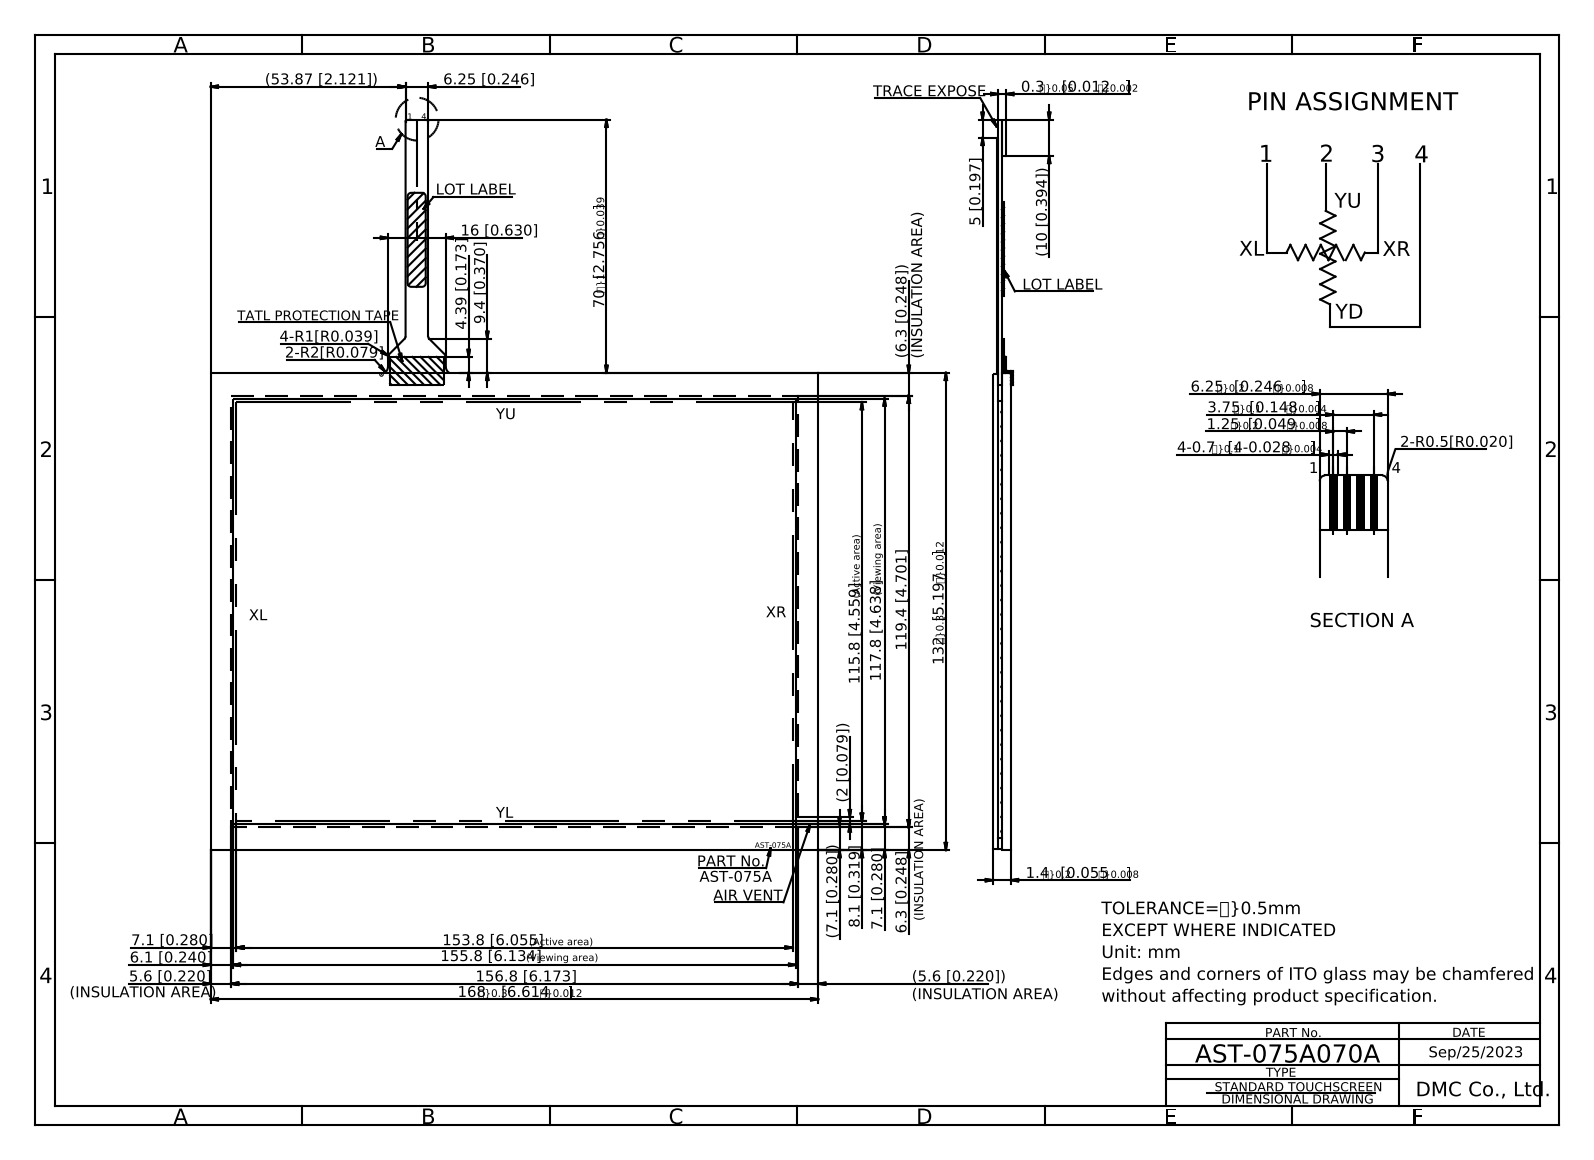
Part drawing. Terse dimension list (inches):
name: AST-075A070A
written by: Autodesk Inventor 2020 (CONFIG_CONTROL_DESIGN)
unit: in
bodies: 1 solid, 51 faces (45 planar, 6 cylindrical, 0 other)
size: 9.26 × 8.992 × 0.053
volume: 1.828 in³; area: 71.77 in²
rounds: 4× R0.039, 2× R0.02
face distances: 0.053, 0.049, 0.045, 0.041, 5.197, 6.614, 0.03, 0.016, 0.02, 0.024
